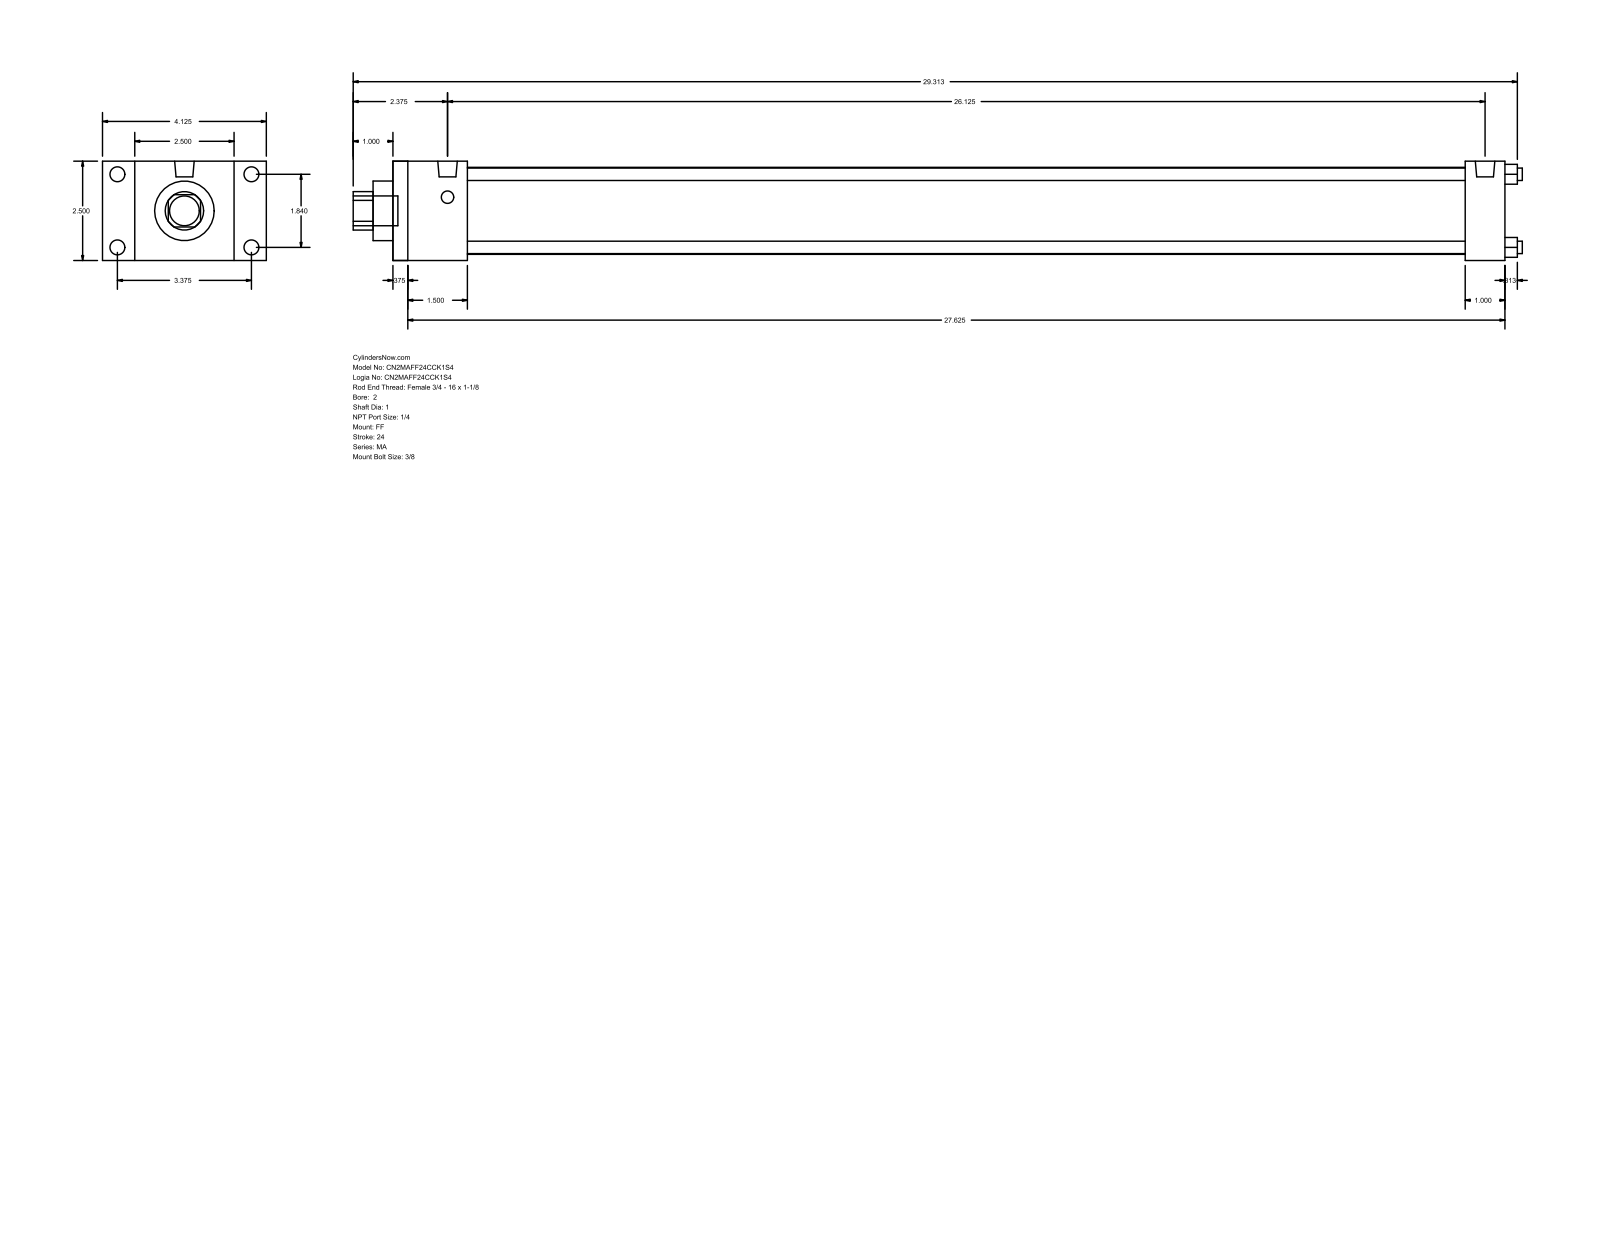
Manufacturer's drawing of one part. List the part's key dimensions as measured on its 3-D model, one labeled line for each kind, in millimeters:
Part name (STEP PRODUCT): MA_FF__0200_1
STEP written by: GSSL Pune (CONFIG_CONTROL_DESIGN)
Units: millimetres
Bodies: 0 solids, 92 faces (64 planar, 28 cylindrical, 0 other)
Overall size (bounding box): 747.71 × 104.78 × 63.5
Round holes (diameter × count): ⌀7.94 ×4, ⌀25.4 ×1, ⌀38.1 ×1, ⌀55.63 ×1
Round bosses / shafts (diameter × count): ⌀9.53 ×4, ⌀7.94 ×4, ⌀12.49 ×2, ⌀19.05 ×1
Partial cylindrical surfaces — rounded edges, fillets, slot ends (radius × count): R12.29 ×1
Main face-to-face distances: 63.5, 711.2, 9.52, 701.68, 25.4, 20.64, 12.7, 47.63, 685.8, 38.11
Hole centre spacings: 33.05, 46.74, 66.1
